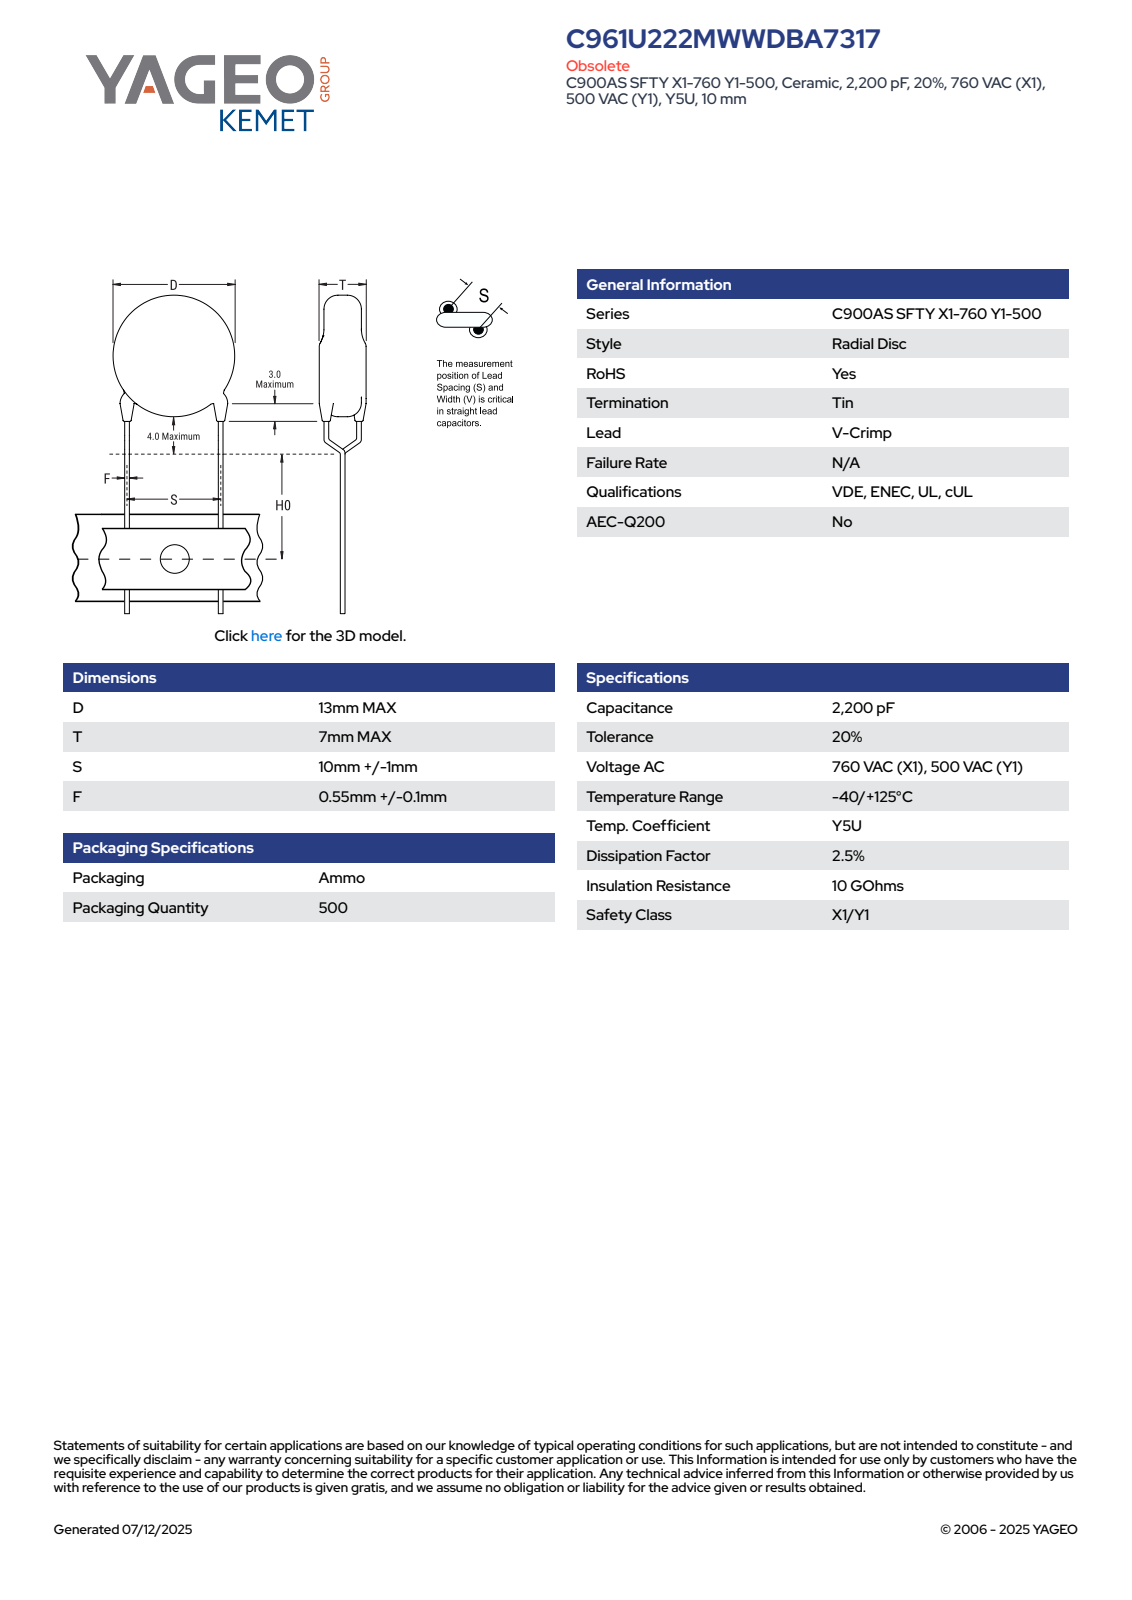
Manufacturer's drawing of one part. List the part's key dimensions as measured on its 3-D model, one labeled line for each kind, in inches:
Part name (STEP PRODUCT): CCD_VCC900_D13T7S10LL20F0.65
STEP written by: SolidWorks 2014 (AUTOMOTIVE_DESIGN)
Units: inches
Bodies: 5 solids, 95 faces (66 planar, 17 cylindrical, 12 other)
Overall size (bounding box): 1.449 × 0.512 × 0.276
Volume: 0.057 in³ · Surface area: 0.997 in²
Round bosses / shafts (diameter × count): ⌀0.026 ×6, ⌀0.512 ×1
Main face-to-face distances: 0.276, 0.902, 0.077, 1.226, 0.324, 1.159, 0.258, 0.067, 0.018, 0.272
